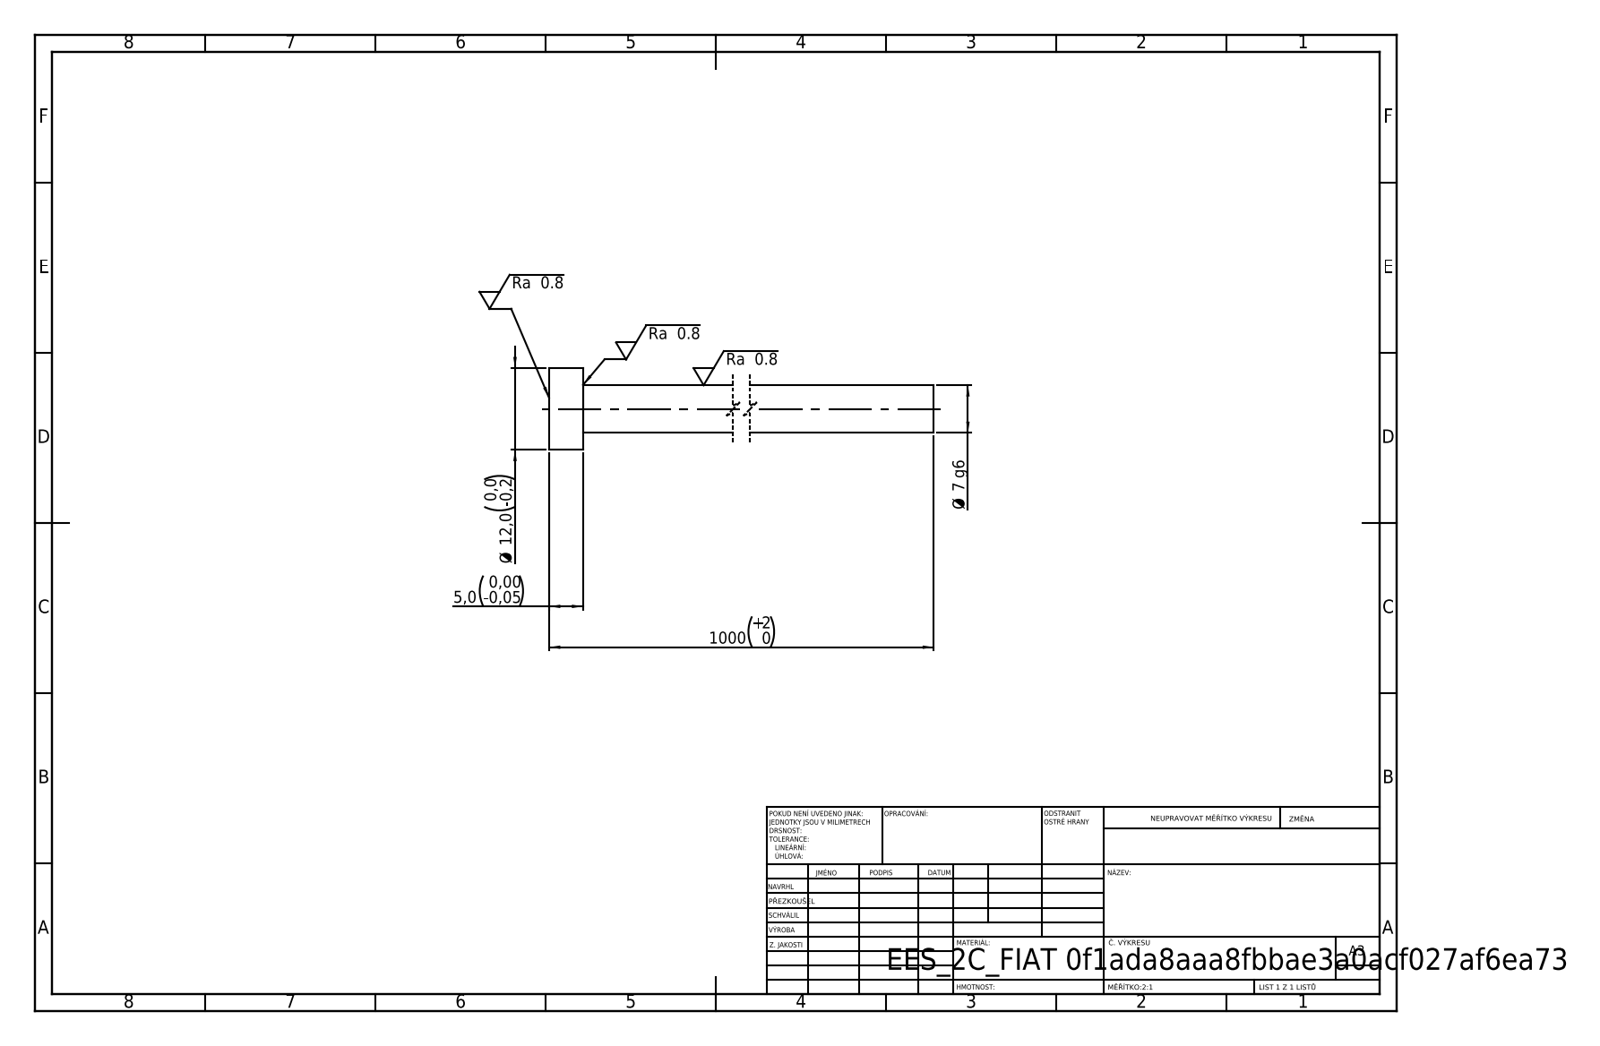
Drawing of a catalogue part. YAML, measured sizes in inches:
step_written_by: "SolidWorks 2019 (CONFIG_CONTROL_DESIGN)"
units: inches
bodies: {solids: 1, faces: 7, planar: 3, cylindrical: 4, other: 0}
overall_size: [39.37, 0.472, 0.472]
volume: 2.371
surface_area: 34.56
round_bosses_or_shafts:
  - {diameter: 0.472, count: 1}
  - {diameter: 0.276, count: 1}
face_to_face_distances: [0.197, 39.37, 39.173]
